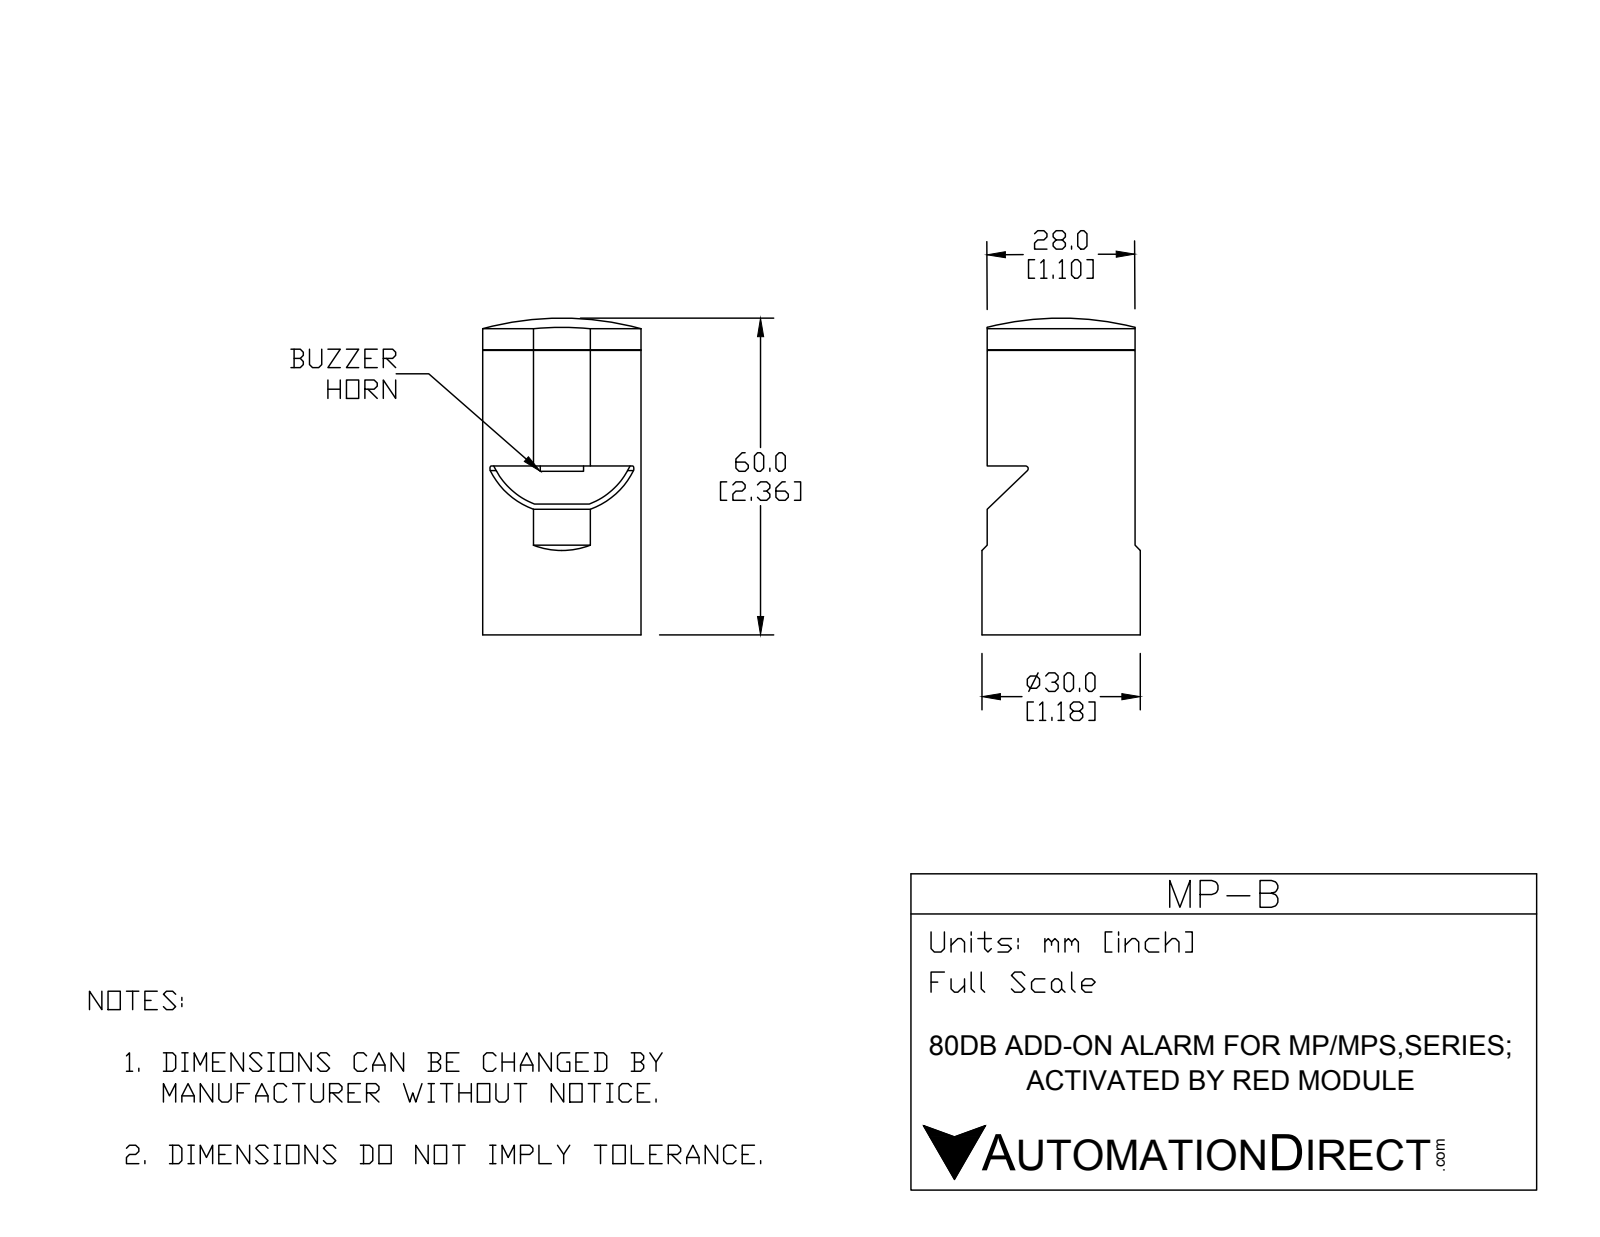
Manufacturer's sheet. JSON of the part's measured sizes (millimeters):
{"part_name": "MP-B", "step_written_by": "SolidWorks 2016 (AUTOMOTIVE_DESIGN)", "units": "millimeters", "bodies": {"solids": 1, "faces": 47, "planar": 26, "cylindrical": 18, "other": 3}, "overall_size": [60, 30, 30], "volume_mm3": 38272, "surface_area_mm2": 7714, "round_holes": [[3.5, 1], [6, 1], [27, 1]], "round_bosses_or_shafts": [[30, 1], [8, 1]], "partial_cylinders_radius": [[0.5, 1], [0.7, 1], [14.9, 1]], "face_to_face_distances": [28, 29.2, 19.5, 8.5, 2.8, 32, 22, 24.8, 7.2, 1]}
